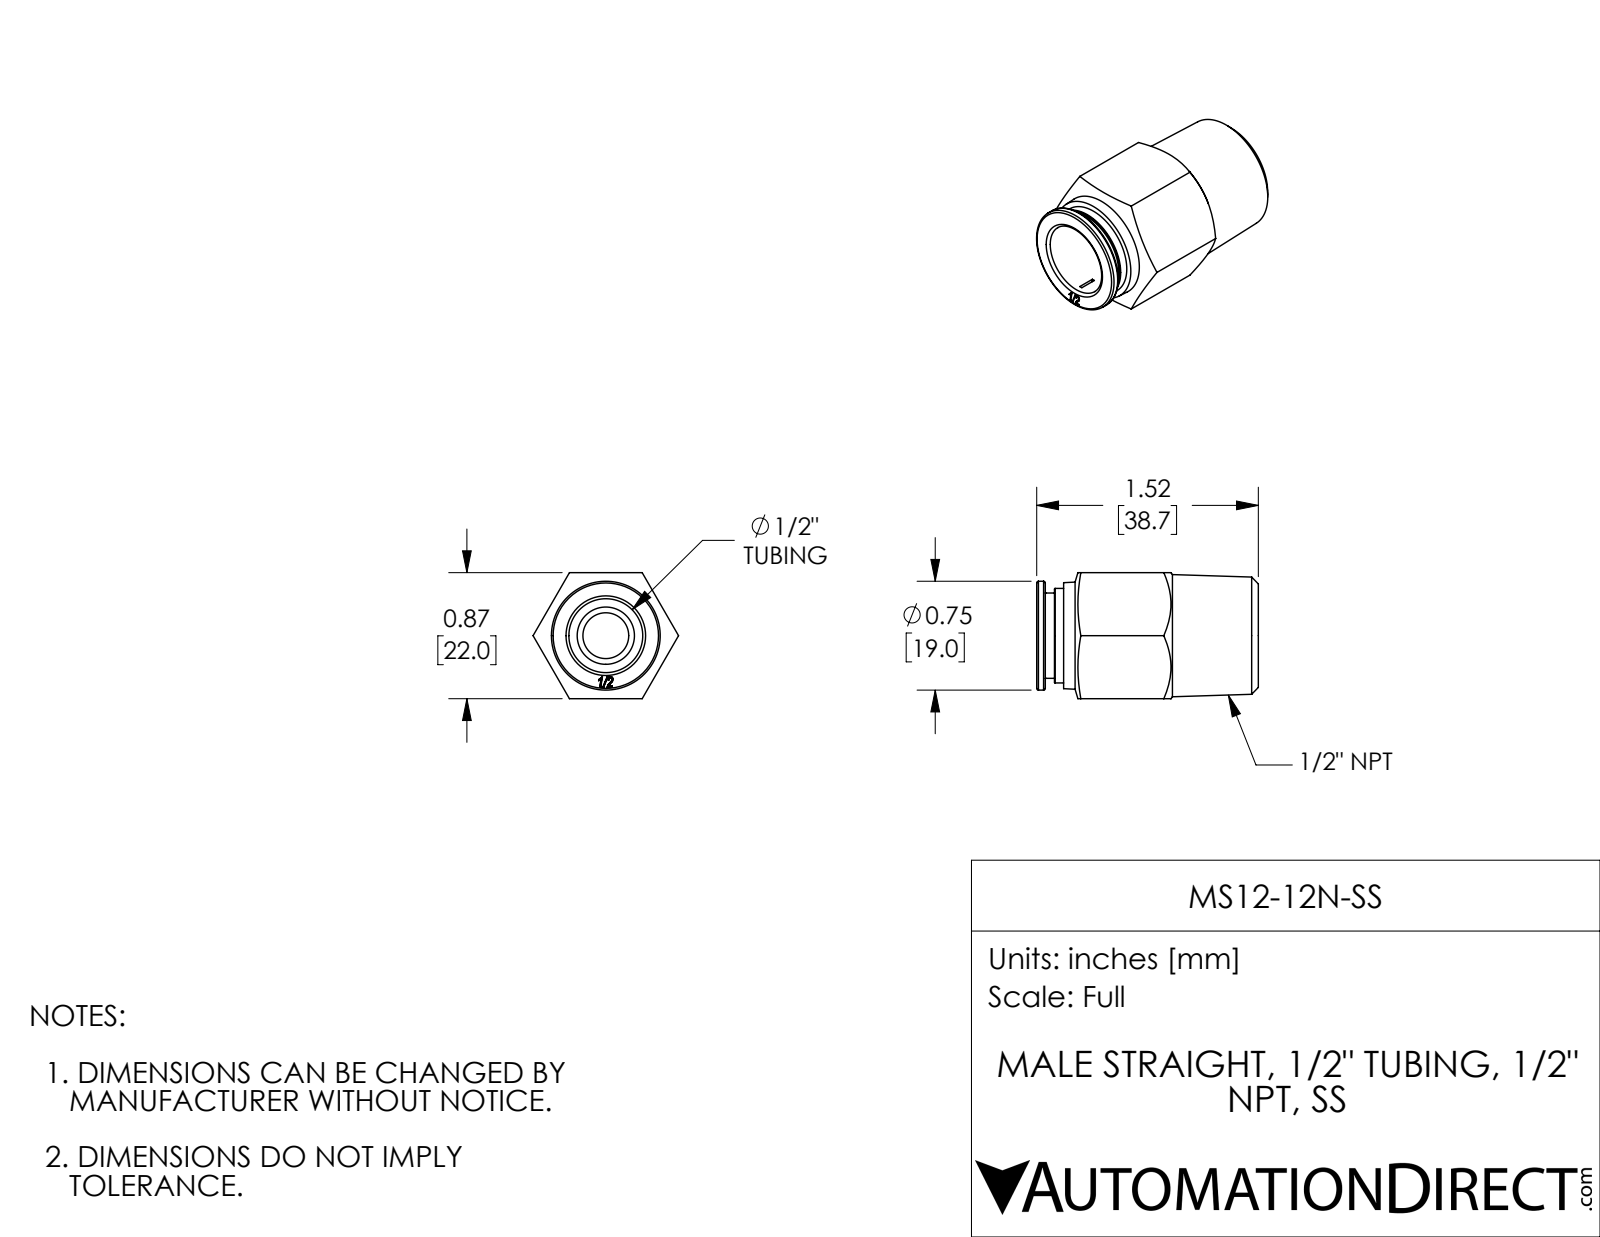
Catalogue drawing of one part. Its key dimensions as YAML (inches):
part_name: "MS12-12N-SS"
step_written_by: "SolidWorks 2017 (AUTOMOTIVE_DESIGN)"
units: inches
bodies: {solids: 1, faces: 87, planar: 35, cylindrical: 12, other: 40}
overall_size: [1.524, 1, 0.866]
volume: 0.61
surface_area: 7.511
round_holes:
  - {diameter: 0.315, count: 1}
  - {diameter: 0.508, count: 1}
  - {diameter: 0.594, count: 1}
round_bosses_or_shafts:
  - {diameter: 0.748, count: 1}
  - {diameter: 0.65, count: 1}
  - {diameter: 0.587, count: 1}
face_to_face_distances: [0.866, 1.524, 0.059, 1.465, 1.339, 0.126, 0.185, 0.673, 0.665, 0.791]
